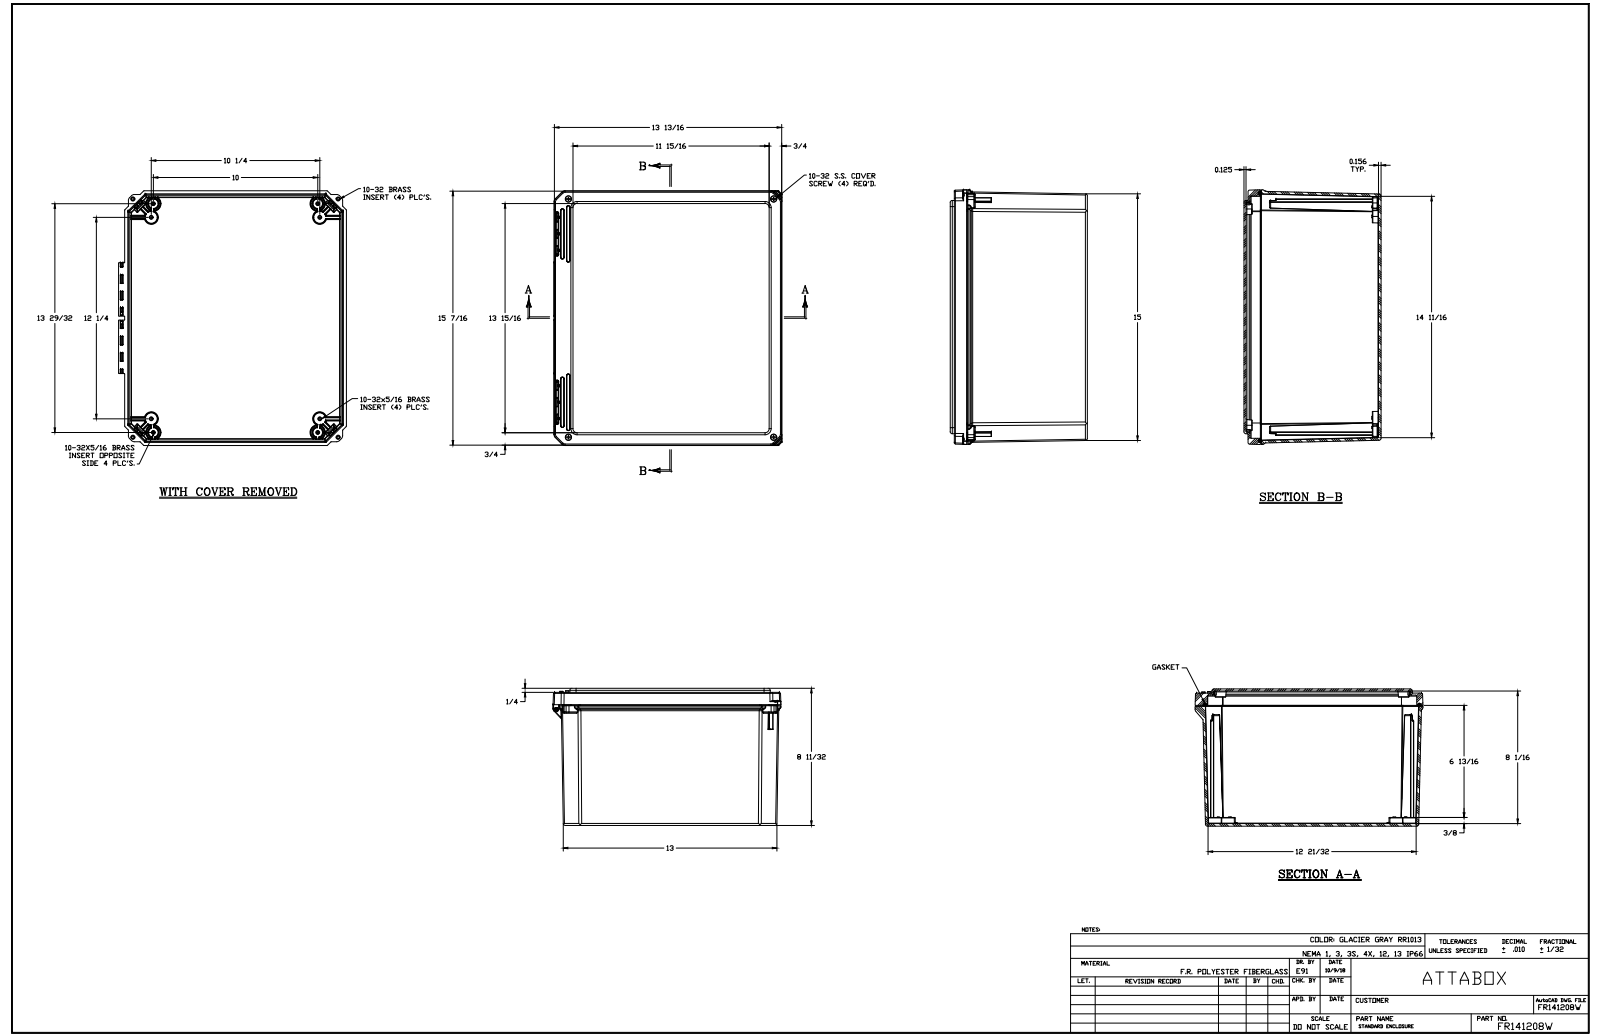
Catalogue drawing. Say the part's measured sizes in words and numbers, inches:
The part is named "FR141208W". Its 3-D file was written by "SolidWorks 2018 (AUTOMOTIVE_DESIGN)". It is 23 solids with 2143 faces: 730 planar, 778 cylindrical and 635 other. Overall it measures 15.497 by 13.864 by 8.341 inches. Its volume is 143.3 cubic inches and its surface area 1 816 square inches. Round holes: 12 of diameter 0.156, 8 of diameter 0.152, 4 of diameter 0.252, 4 of diameter 0.253, 2 of diameter 0.219, 2 of diameter 0.227, 2 of diameter 0.313, 1 of diameter 0.137. Round bosses or shafts: 12 of diameter 0.246, 4 of diameter 0.45, 4 of diameter 0.199, 2 of diameter 0.435. Partial cylindrical surfaces (rounded edges, fillets, slot ends): 175 of radius 0.01, 88 of radius 0.005, 49 of radius 0.02, 43 of radius 0.03, 24 of radius 0.03, 24 of radius 0.09, 24 of radius 0.096, 22 of radius 0.125. The main face-to-face distances are 0.156, 0.125, 8.185, 8.341, 0.16, 0.159, 8.217, 8.061, 0.25, 0.125. The hole center spacings are 1.584, 11.249, 11.425, 0.828, 1.281, 10.158, 12.25, 12.489.
